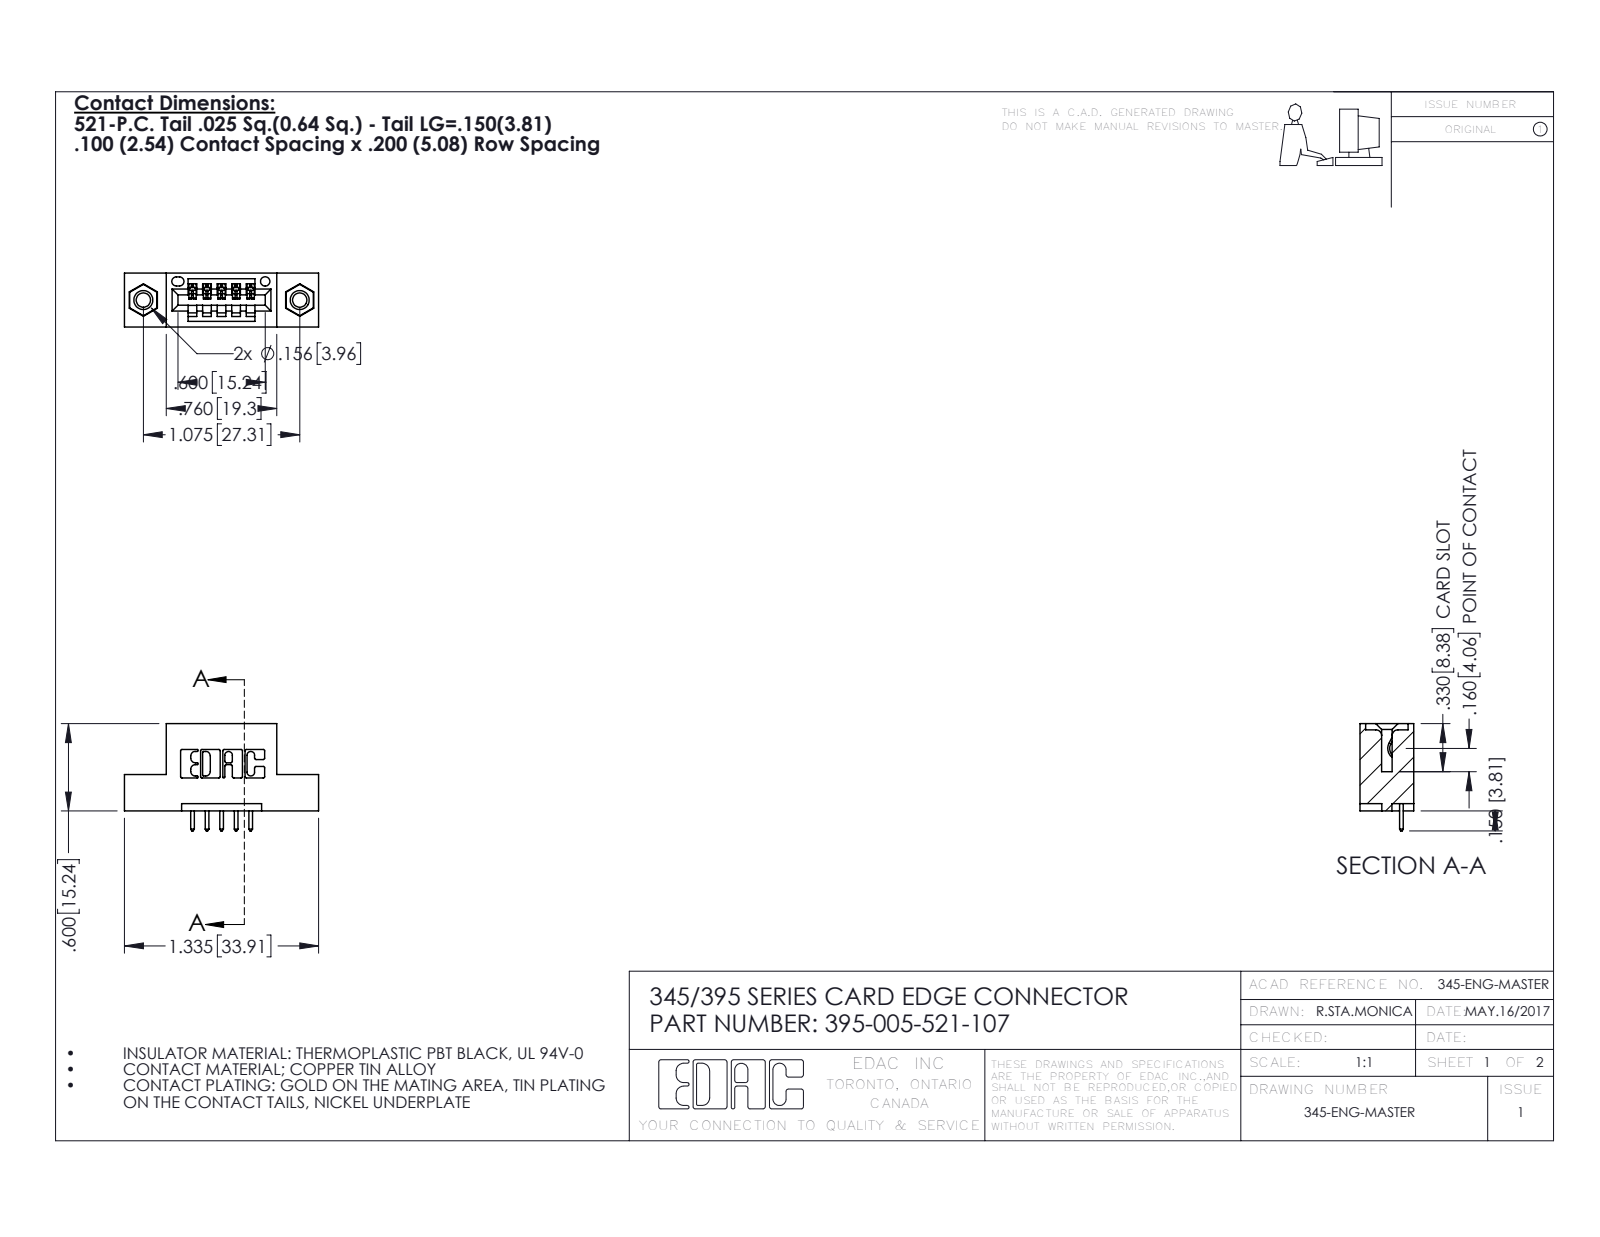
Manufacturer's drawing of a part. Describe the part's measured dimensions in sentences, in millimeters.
The part is named "395-005-521-107; 345-292-001_345-293-121; 345 Part_Flush Mounting Lugs - 0.156 Dia-TI; 345-250-001_345-250-005-103". Its 3-D file was written by "SolidWorks 2016 (CONFIG_CONTROL_DESIGN)". It is 8 solids with 476 faces: 312 planar, 148 cylindrical and 16 other. Overall it measures 33.9 by 18.7 by 9.4 millimeters. Its volume is 2 880 cubic millimeters and its surface area 3 314 square millimeters. Round holes: 2 of diameter 2.5, 2 of diameter 3.2, 2 of diameter 4, 1 of diameter 1.6. Round bosses or shafts: 2 of diameter 3.9. Partial cylindrical surfaces (rounded edges, fillets, slot ends): 22 of radius 0.3, 10 of radius 0.2, 10 of radius 0.3, 6 of radius 0.2, 6 of radius 0.8, 3 of radius 0.7, 2 of radius 0.8, 2 of radius 1. The main face-to-face distances are 5.1, 9.4, 1.8, 7.6, 2.5, 0.6, 8.9, 6.4, 2.5, 6.9. The hole center spacings are 6.9, 21.5, 27.3.
